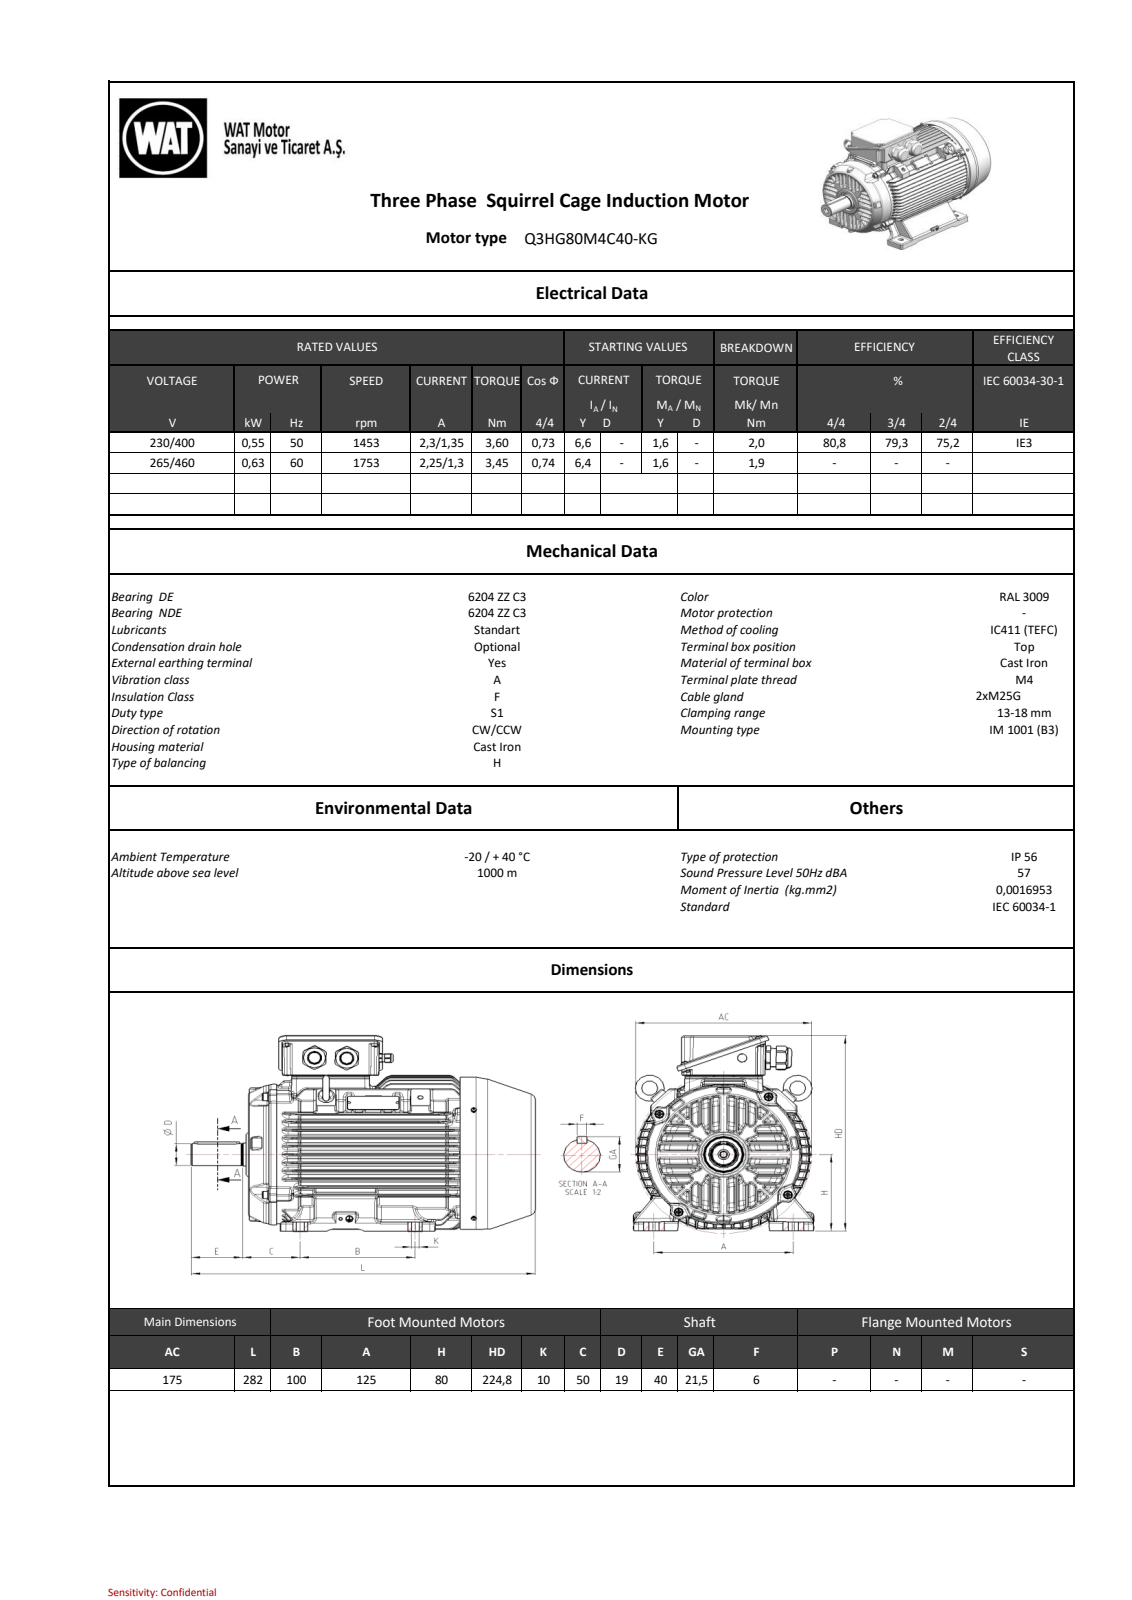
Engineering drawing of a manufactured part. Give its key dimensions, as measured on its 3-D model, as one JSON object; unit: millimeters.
{"part_name": "C901B65877A5yh61", "step_written_by": "SIEMENS PLM Software NX 11.0 (AUTOMOTIVE_DESIGN)", "units": "millimeters", "bodies": {"solids": 0, "faces": 3024, "planar": 809, "cylindrical": 861, "other": 1354}, "overall_size": [281.76, 224.98, 221.33], "round_holes": [[10, 3], [2.5, 2], [4.2, 2], [17.2, 2], [5, 1], [6.4, 1], [6.5, 1], [27.8, 1], [28, 1], [168, 1]], "round_bosses_or_shafts": [[20, 4], [8.65, 3], [8.5, 3], [8, 3], [5, 3], [27.7, 2], [25.25, 2], [9.2, 2]], "partial_cylinders_radius": [[1.5, 319], [2, 55], [2.5, 40], [1, 30], [4, 26], [0.2, 23], [5, 22], [26.5, 12]], "face_to_face_distances": [41.78, 62.56, 3.01, 1.5, 234.61, 192.83, 152.95, 215.51, 5, 3], "hole_center_spacings": [40, 74.99, 115.35]}
